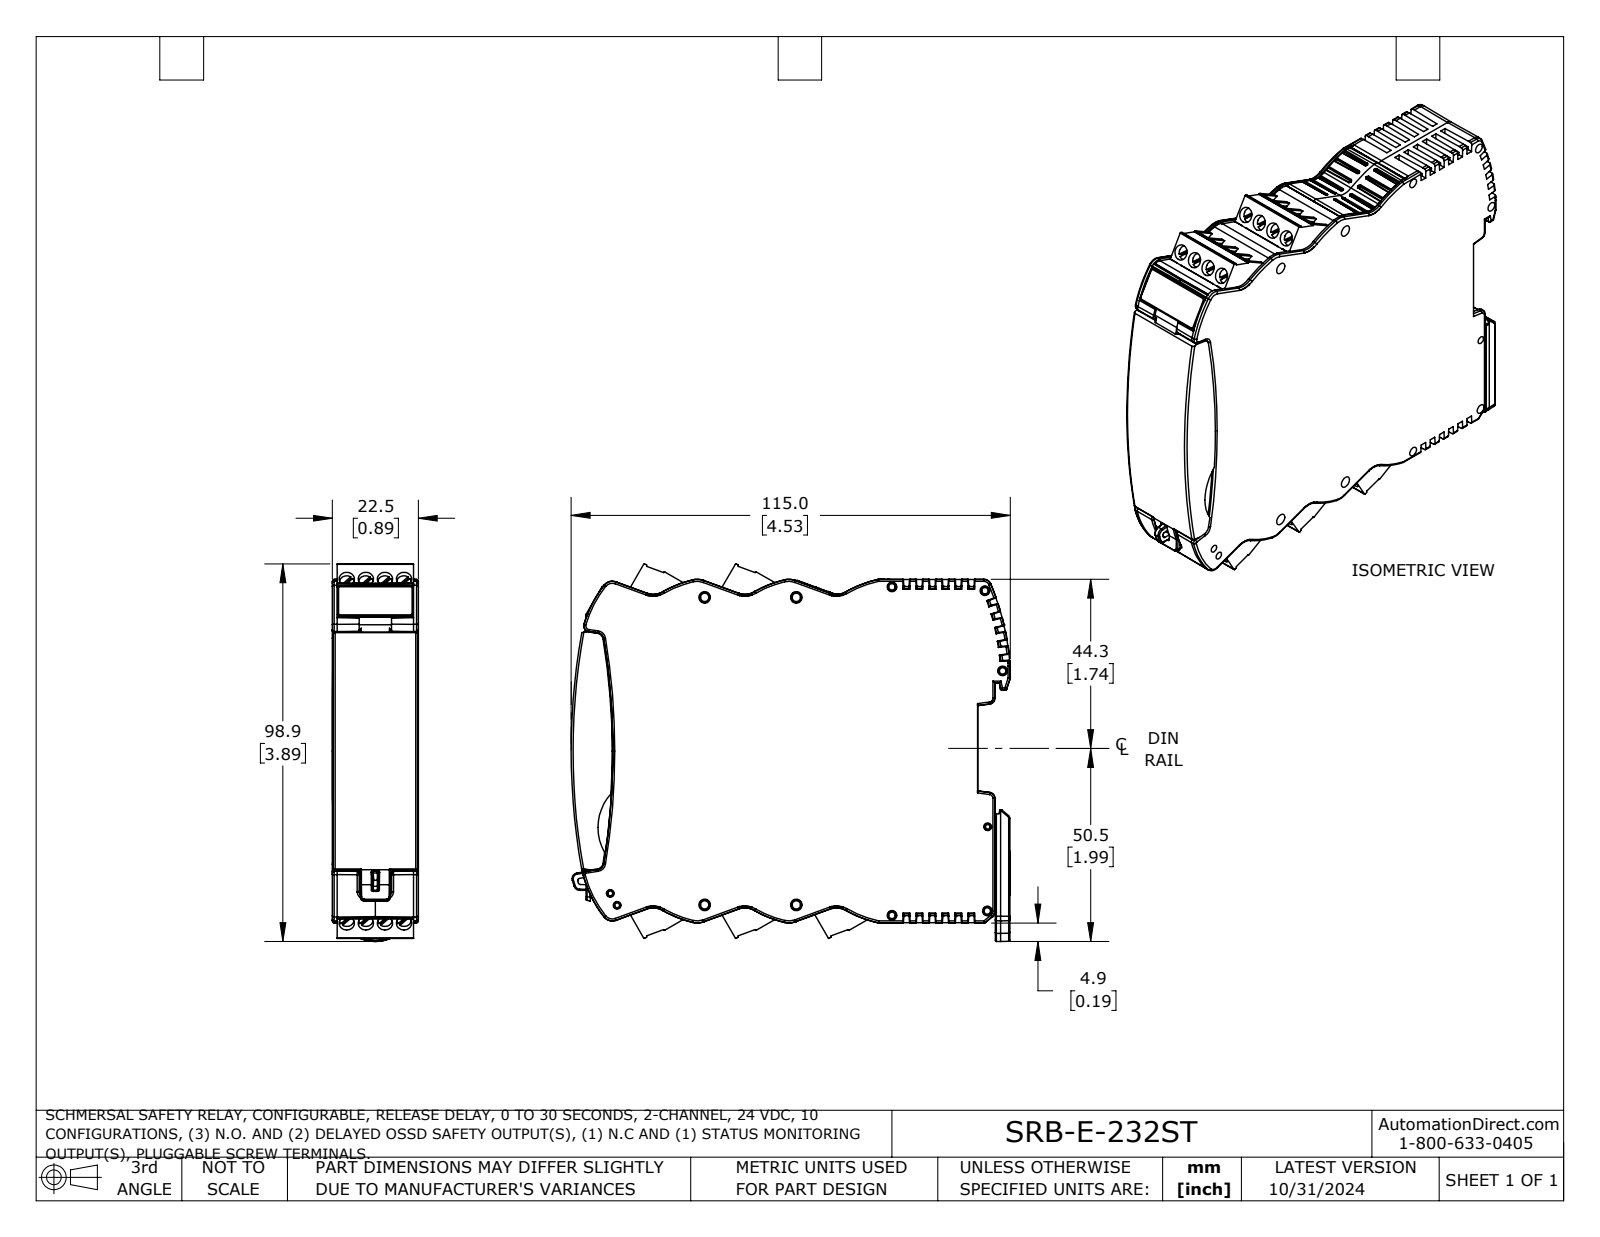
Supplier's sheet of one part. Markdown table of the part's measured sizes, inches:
| quantity | value |
| --- | --- |
| part name | SRB-E-232ST |
| STEP written by | SolidWorks 2023 (AUTOMOTIVE_DESIGN) |
| units | inches |
| bodies | 2 solids, 3149 faces (1698 planar, 731 cylindrical, 720 other) |
| overall size | 4.528 × 3.893 × 0.886 |
| volume | 12.97 in³ |
| surface area | 65.25 in² |
| round holes (diameter × count) | 0.157 × 20 |
| round bosses / shafts (diameter × count) | 0.149 × 20, 0.067 × 1 |
| partial cylindrical surfaces (radius × count) | 0.012 × 174, 0.02 × 121, 0.01 × 60, 0.008 × 45, 0.059 × 26, 0.039 × 20, 0.007 × 10, 0.079 × 8 |
| main face-to-face distances | 0.886, 0.049, 0.837, 0.133, 0.035, 0.267, 0.134, 0.014, 0.85, 0.801 |
| hole center spacings | 0.197, 0.512, 0.394, 0.472, 0.615, 0.518, 0.972, 0.591 |
